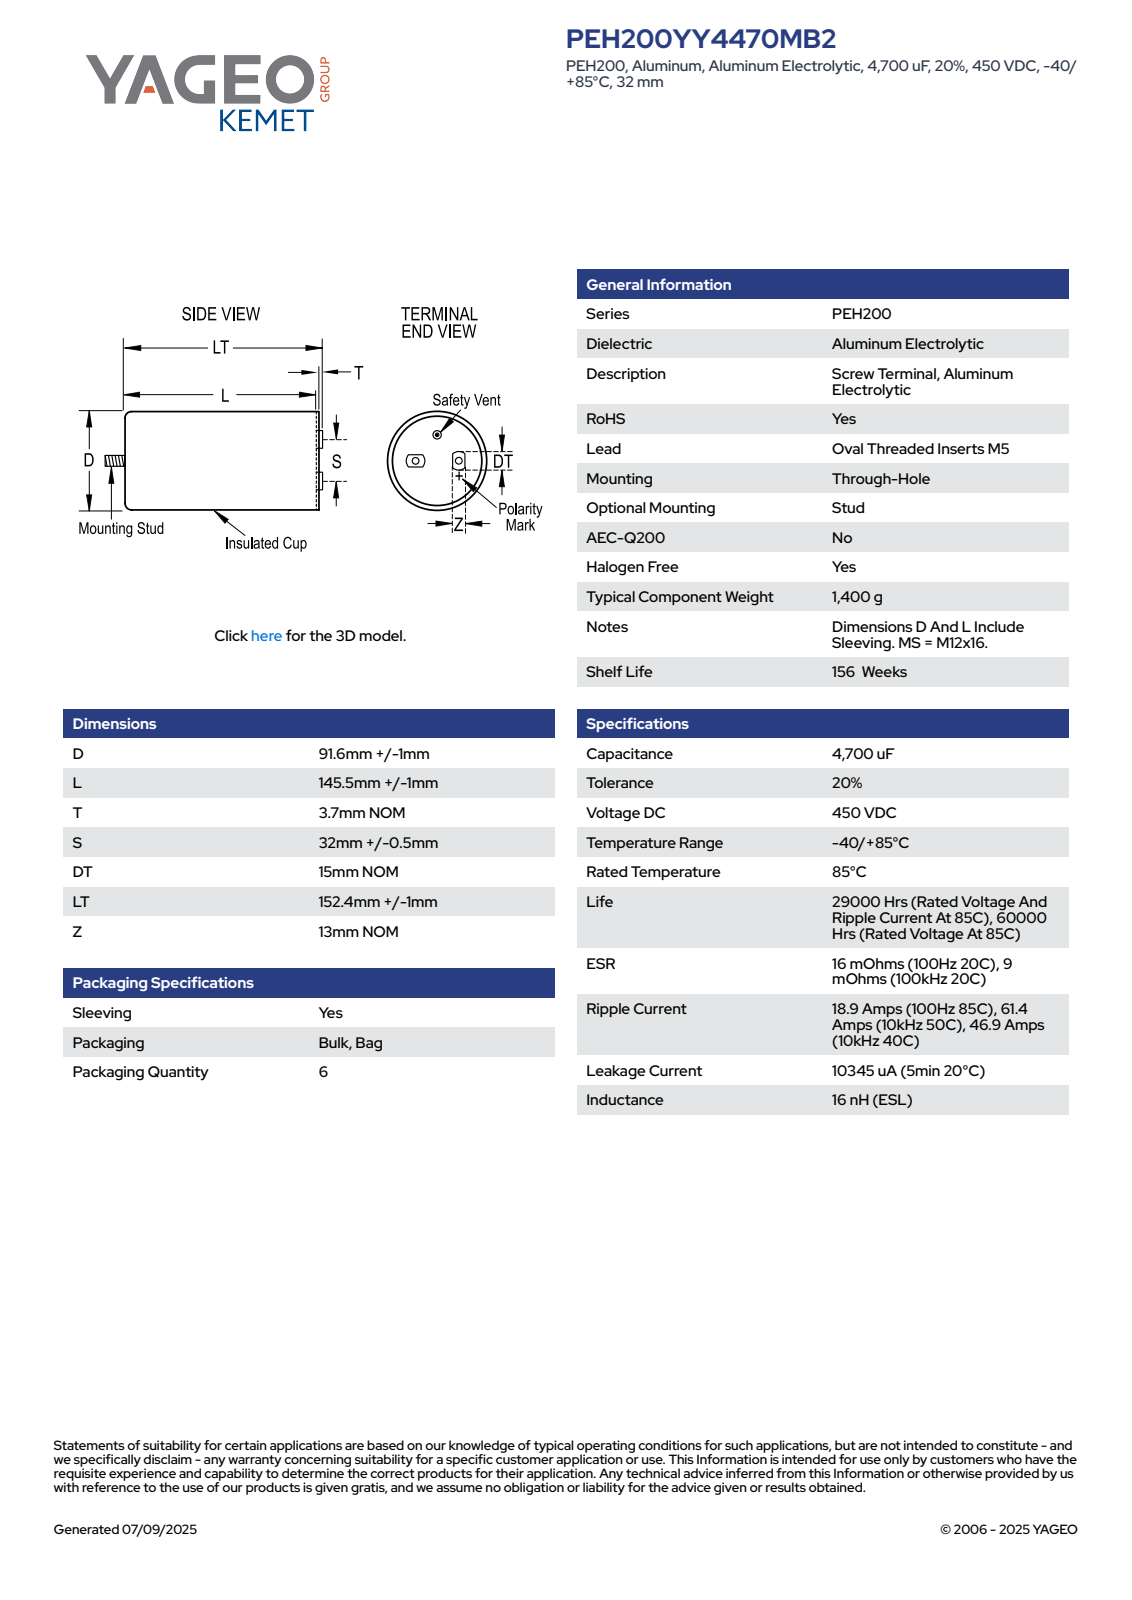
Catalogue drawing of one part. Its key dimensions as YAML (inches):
part_name: "Can_24; CARCS_D92.6L146.5S32T3.7; Oval_Terminal_24; Stud"
step_written_by: "SolidWorks 2014 (AUTOMOTIVE_DESIGN)"
units: inches
bodies: {solids: 4, faces: 185, planar: 70, cylindrical: 83, other: 32}
overall_size: [6.669, 3.646, 3.646]
volume: 60.47
surface_area: 93.38
round_holes:
  - {diameter: 0.158, count: 2}
  - {diameter: 3.567, count: 1}
round_bosses_or_shafts:
  - {diameter: 0.295, count: 2}
  - {diameter: 3.646, count: 1}
  - {diameter: 0.472, count: 1}
  - {diameter: 0.457, count: 1}
partial_cylinders:
  - {radius: 0.295, count: 2}
  - {radius: 1.822, count: 1}
face_to_face_distances: [5.768, 0.126, 0.272, 6.039, 5.894, 0.146, 0.197, 6.669, 6.524, 6.398]
hole_center_spacings: [0.63, 1.26]
